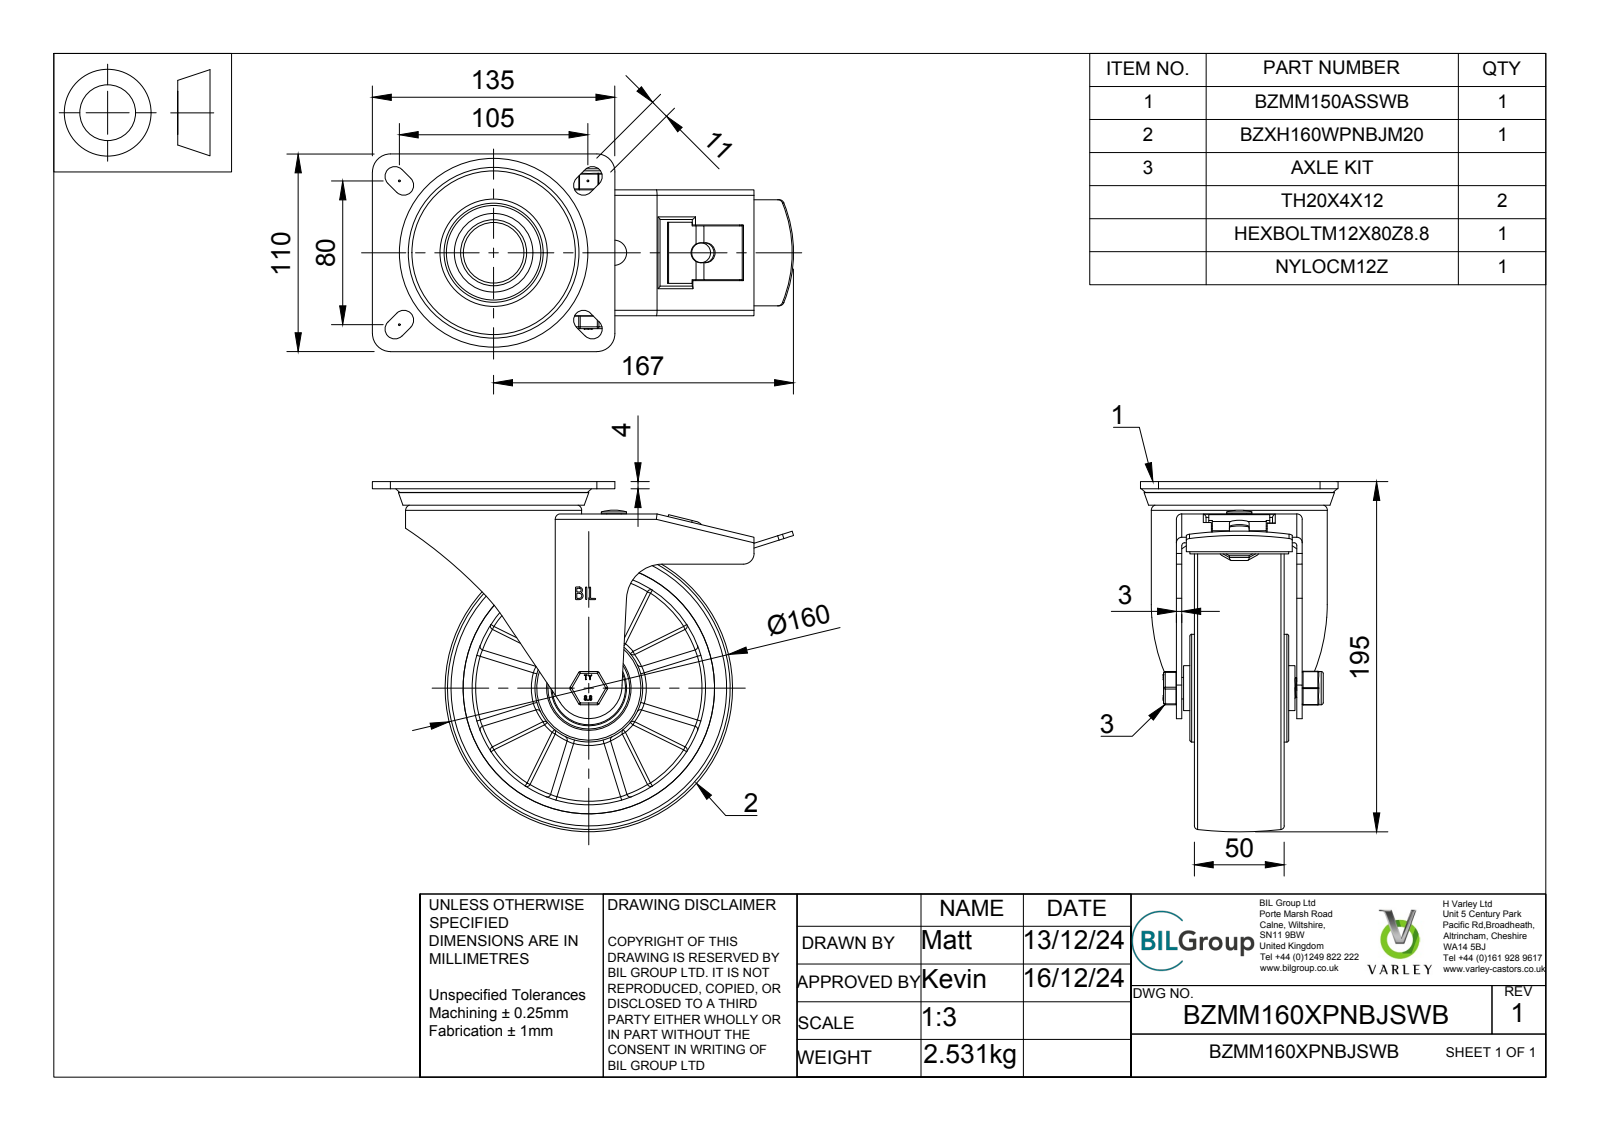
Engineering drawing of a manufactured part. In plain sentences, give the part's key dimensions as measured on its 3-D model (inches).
The part is named "BZMM160XPNBJSWB v4; BZMM150ASSWB - 64 v1; ZINC PLATED, PRESSED STEEL TOP PLATE; ZINC PLATED, PRESSED STEEL TOP PLATE Geometry (+7 more)". Its 3-D file was written by "Autodesk Translation Framework v13.20.0.188 (AP242_MANAGED_MODEL_BASED_3D_ENGINEERING_MIM_LF)". It is 82 solids with 1462 faces: 547 planar, 254 cylindrical and 661 other. Overall it measures 9.232 by 7.677 by 4.331 inches. Its volume is 49.73 cubic inches and its surface area 522.6 square inches. Round holes: 1 of diameter 0.315, 1 of diameter 0.433, 1 of diameter 0.472, 1 of diameter 0.48, 1 of diameter 0.551, 1 of diameter 0.787, 1 of diameter 0.827, 1 of diameter 1.122, 1 of diameter 1.213, 1 of diameter 1.329, 1 of diameter 1.565, 1 of diameter 1.587. Round bosses or shafts: 1 of diameter 3.858, 1 of diameter 3.071, 1 of diameter 2.362, 1 of diameter 1.969, 1 of diameter 1.606, 1 of diameter 1.232, 1 of diameter 1.063, 1 of diameter 1.024. Partial cylindrical surfaces (rounded edges, fillets, slot ends): 18 of radius 0.02, 12 of radius 0.039, 10 of radius 0.059, 10 of radius 0.217, 6 of radius 0.01, 6 of radius 0.098, 6 of radius 0.118, 4 of radius 0.394. The main face-to-face distances are 0.354, 0.118, 0.276, 0.472, 0.197, 0.079, 0.157, 0.709, 0.827, 0.394. The hole center spacings are 2.638.
